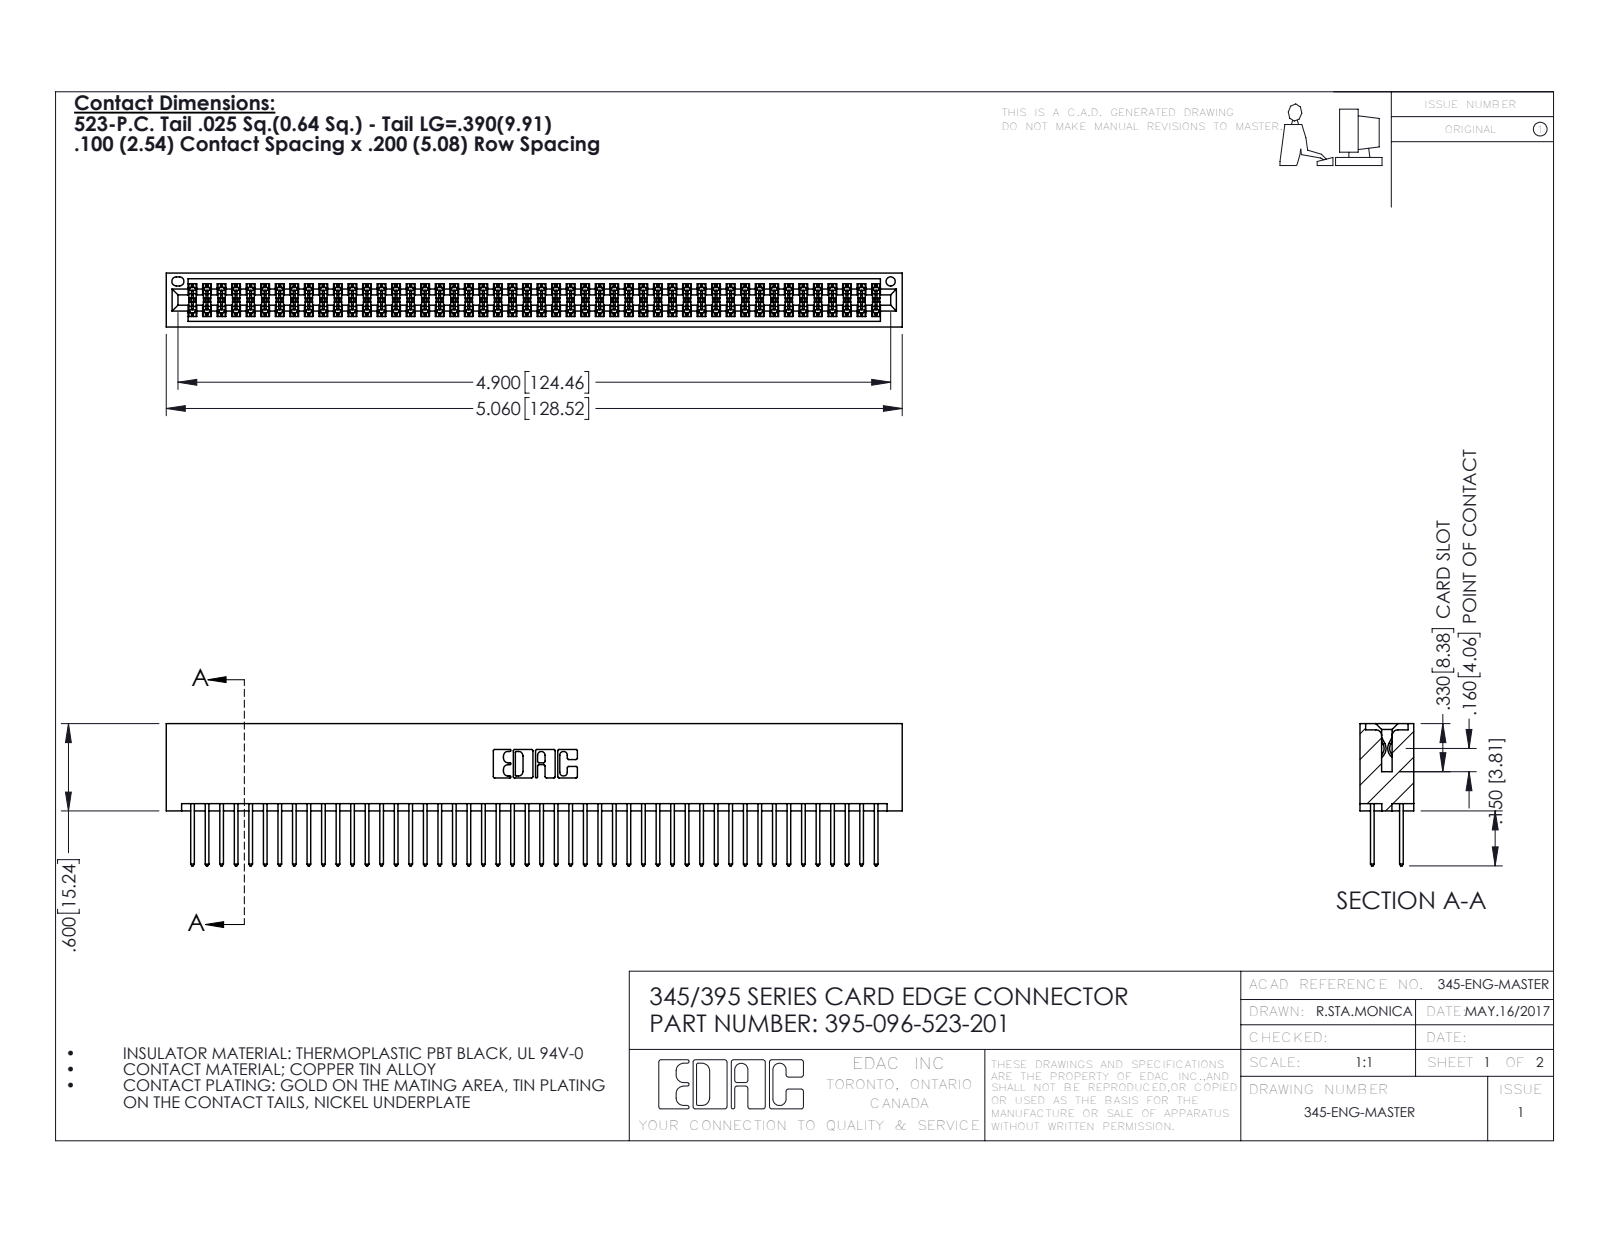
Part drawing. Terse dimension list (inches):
name: 345-292-001_345-293-123; 345 Part_No Mounting Lugs; 395-096-523-201
written by: SolidWorks 2016 (CONFIG_CONTROL_DESIGN)
unit: in
bodies: 97 solids, 4918 faces (3244 planar, 1674 cylindrical, 0 other)
size: 5.06 × 0.977 × 0.37
volume: 0.815 in³; area: 32.61 in²
holes: 1× ⌀0.064
rounds: 144× R0.006, 96× R0.01, 22× R0.01, 6× R0.007, 6× R0.031, 3× R0.026, 2× R0.014, 2× R0.019
face distances: 0.298, 0.072, 0.2, 0.098, 0.272, 0.025, 0.37, 0.225, 0.175, 0.149
